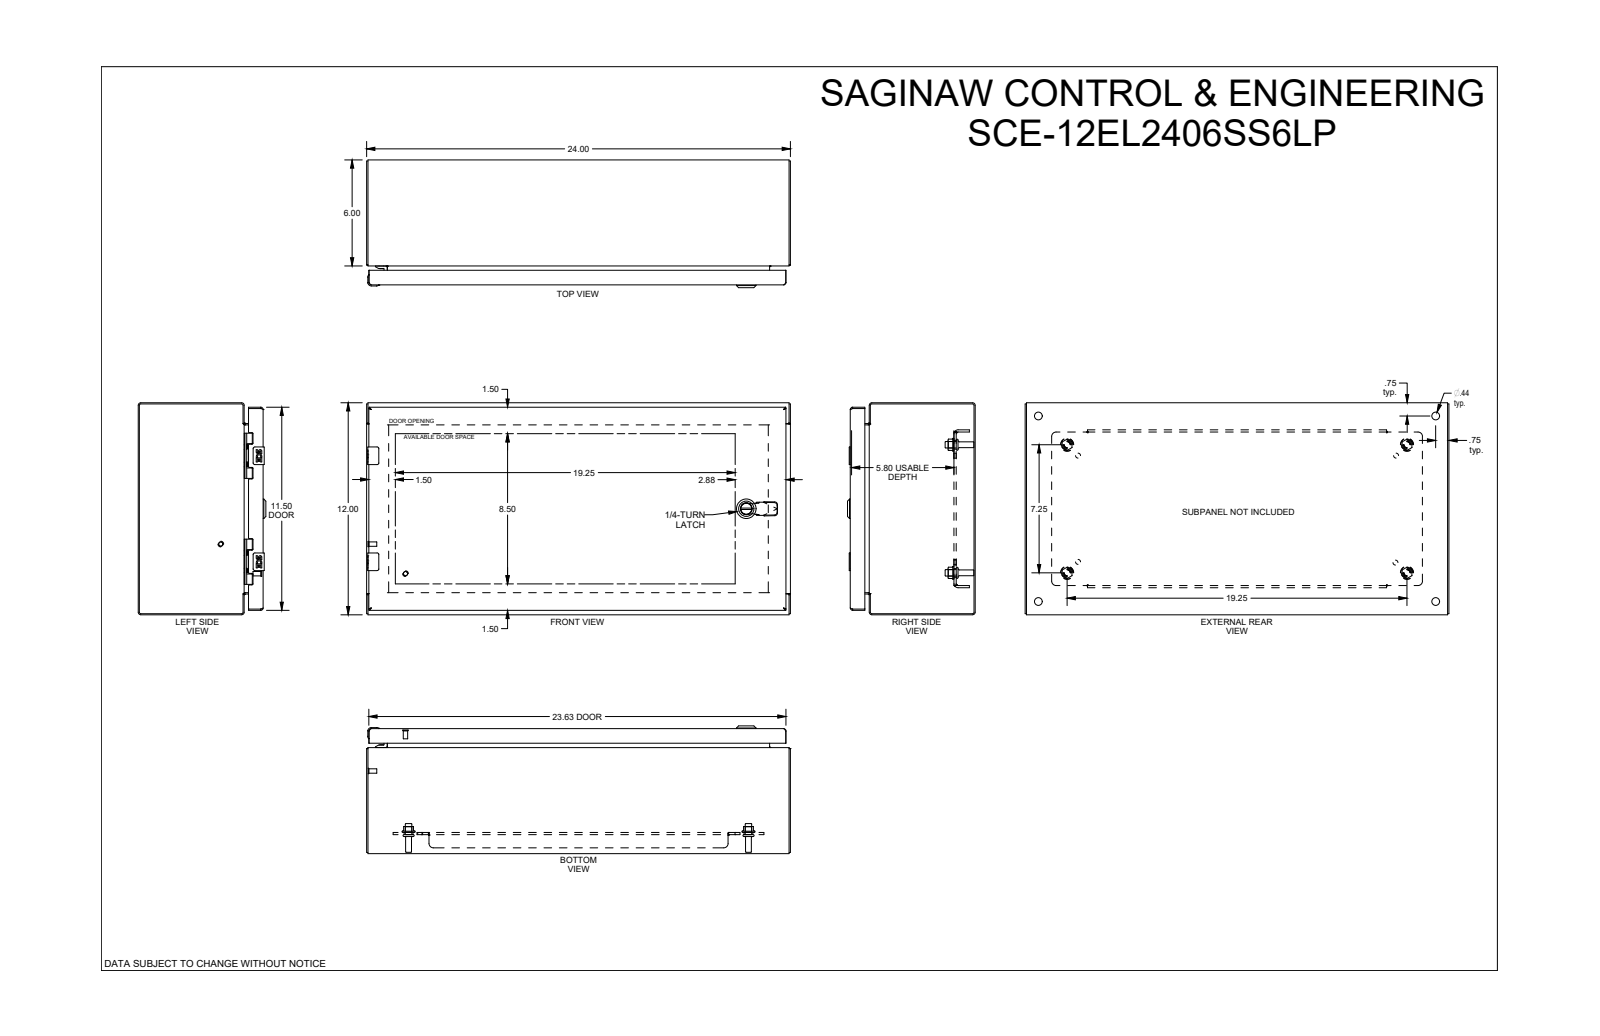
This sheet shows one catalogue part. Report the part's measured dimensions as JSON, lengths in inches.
{"part_name": "SCE-12EL2406LP", "step_written_by": "SolidWorks 2019 (AUTOMOTIVE_DESIGN)", "units": "inches", "bodies": {"solids": 37, "faces": 1695, "planar": 846, "cylindrical": 511, "other": 338}, "overall_size": [24, 12, 7.23], "volume_in3": 121.7, "surface_area_in2": 2935, "round_holes": [[0.172, 4], [0.205, 4], [0.244, 4], [0.266, 4], [0.281, 4], [0.367, 4], [0.375, 4], [0.437, 4], [0.5, 4], [0.04, 2], [0.188, 2], [0.218, 2]], "round_bosses_or_shafts": [[0.17, 6], [0.366, 4], [0.332, 4], [0.25, 4], [0.24, 4], [0.196, 3], [0.248, 2], [1.102, 1]], "partial_cylinders_radius": [[0.012, 30], [0.01, 28], [0.015, 24], [0.06, 13], [0.02, 12], [0.1, 12], [0.031, 10], [0.117, 10]], "face_to_face_distances": [0.075, 0.06, 11.925, 7.073, 6.998, 7.013, 6.938, 1, 0.125, 1.2], "hole_center_spacings": [0.985, 6, 0.02, 0.493, 0.494, 0.875, 2.743, 6.66]}
